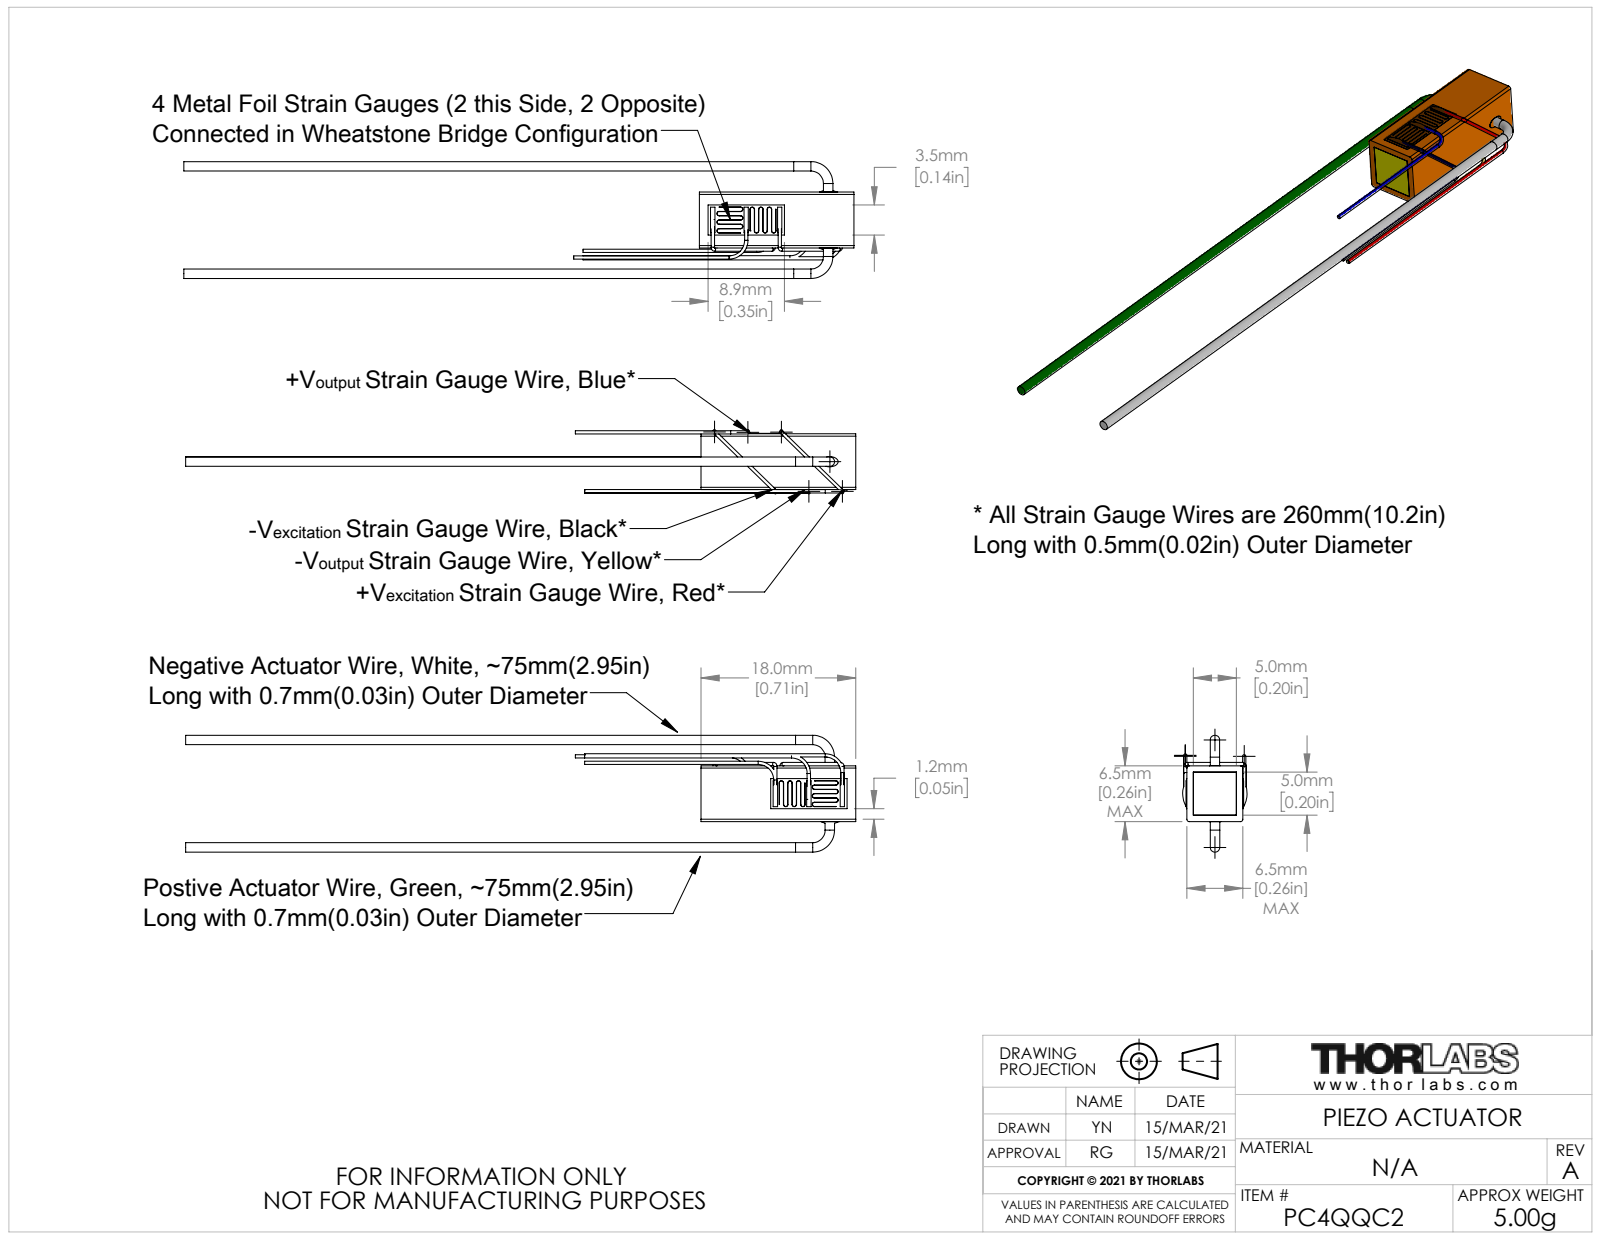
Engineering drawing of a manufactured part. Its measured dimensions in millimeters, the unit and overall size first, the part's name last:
Units: millimetres
Overall size (bounding box): 78.01 × 13.6 × 7.5
Round bosses / shafts (diameter × count): ⌀0.38 ×12, ⌀1.1 ×4
Partial cylindrical surfaces — rounded edges, fillets, slot ends (radius × count): R0.24 ×24, R0.26 ×24, R0.27 ×4
Main face-to-face distances: 0.75, 5.75, 5, 6.5, 0.8, 5.8, 6.55, 18, 6.6, 1.5
Volume: 928 mm³ · Surface area: 2 117 mm²
Bodies: 12 solids, 268 faces (132 planar, 104 cylindrical, 32 other)
Part name (STEP PRODUCT): CTN017169-E0W
STEP written by: SolidWorks 2018 (AUTOMOTIVE_DESIGN)
